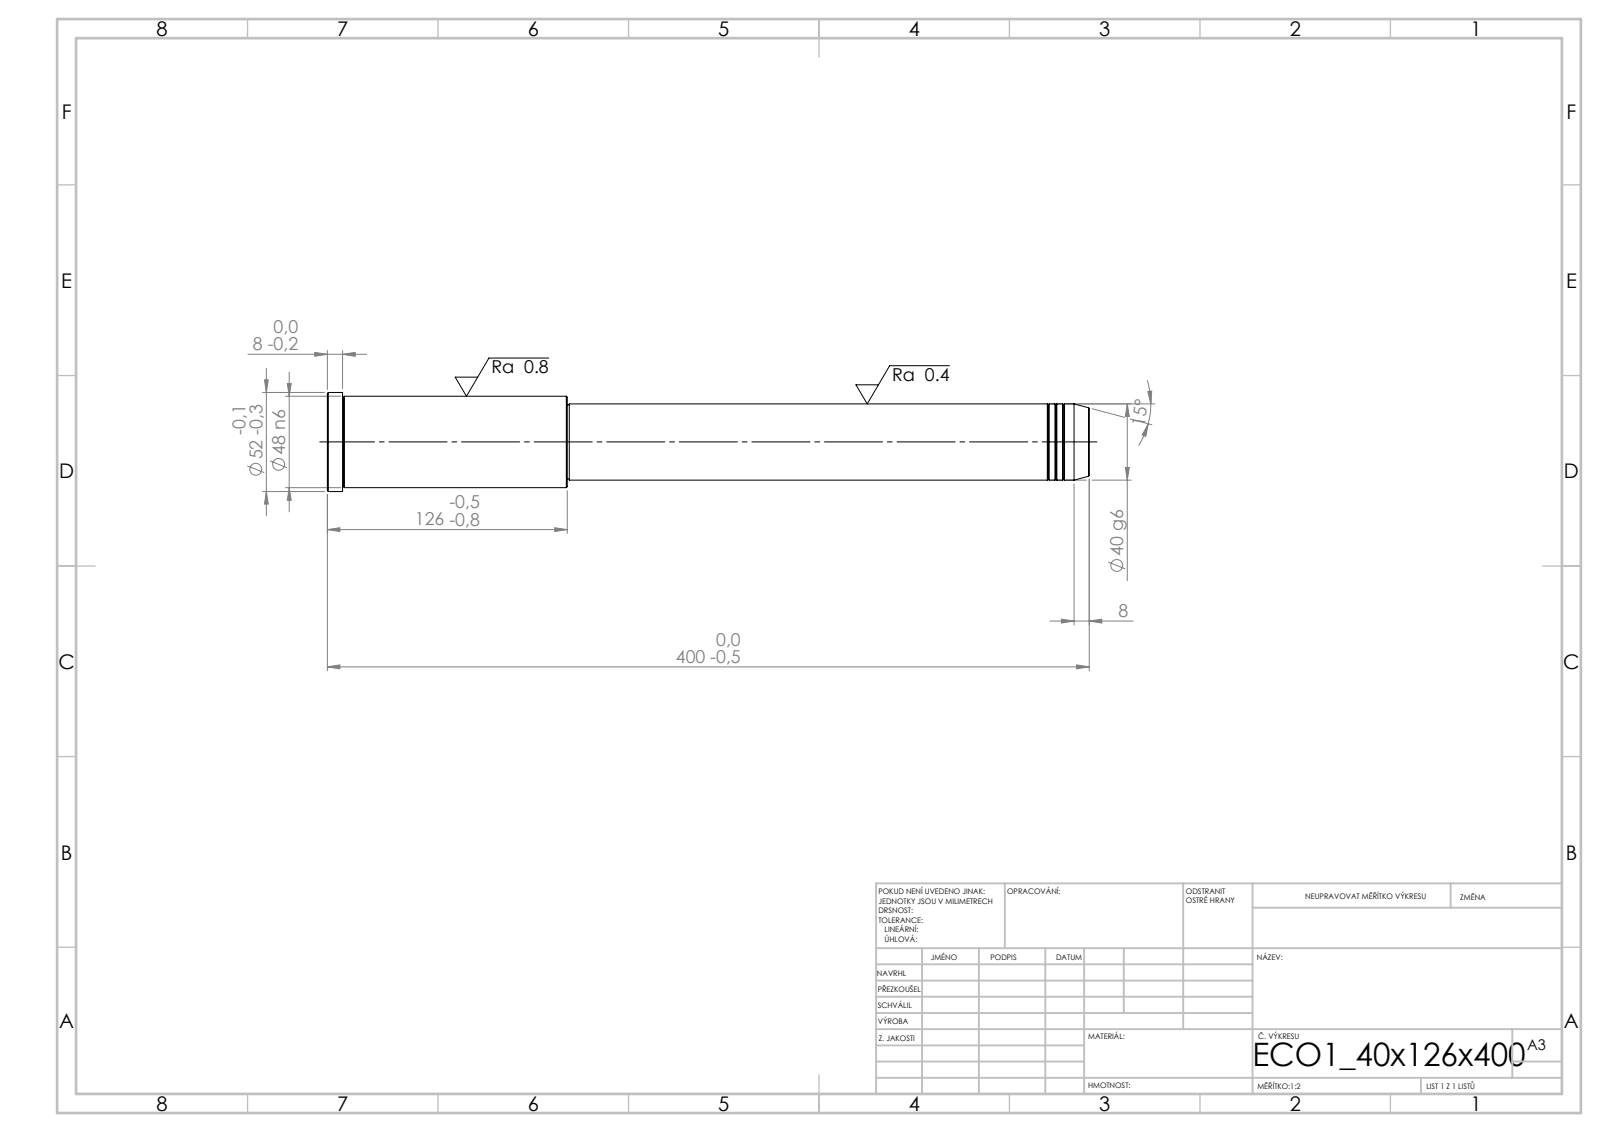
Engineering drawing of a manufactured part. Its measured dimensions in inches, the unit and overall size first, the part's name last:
Units: inches
Overall size (bounding box): 15.748 × 2.047 × 2.047
Round bosses / shafts (diameter × count): ⌀2.047 ×1, ⌀1.89 ×1, ⌀1.575 ×1, ⌀1.535 ×1
Main face-to-face distances: 15.748, 10.787, 4.961, 15.433, 4.646, 0.315, 10.748, 0.039, 4.685, 5
Volume: 35 in³ · Surface area: 89.6 in²
Bodies: 1 solid, 43 faces (5 planar, 14 cylindrical, 24 other)
STEP written by: SolidWorks 2019 (CONFIG_CONTROL_DESIGN)
